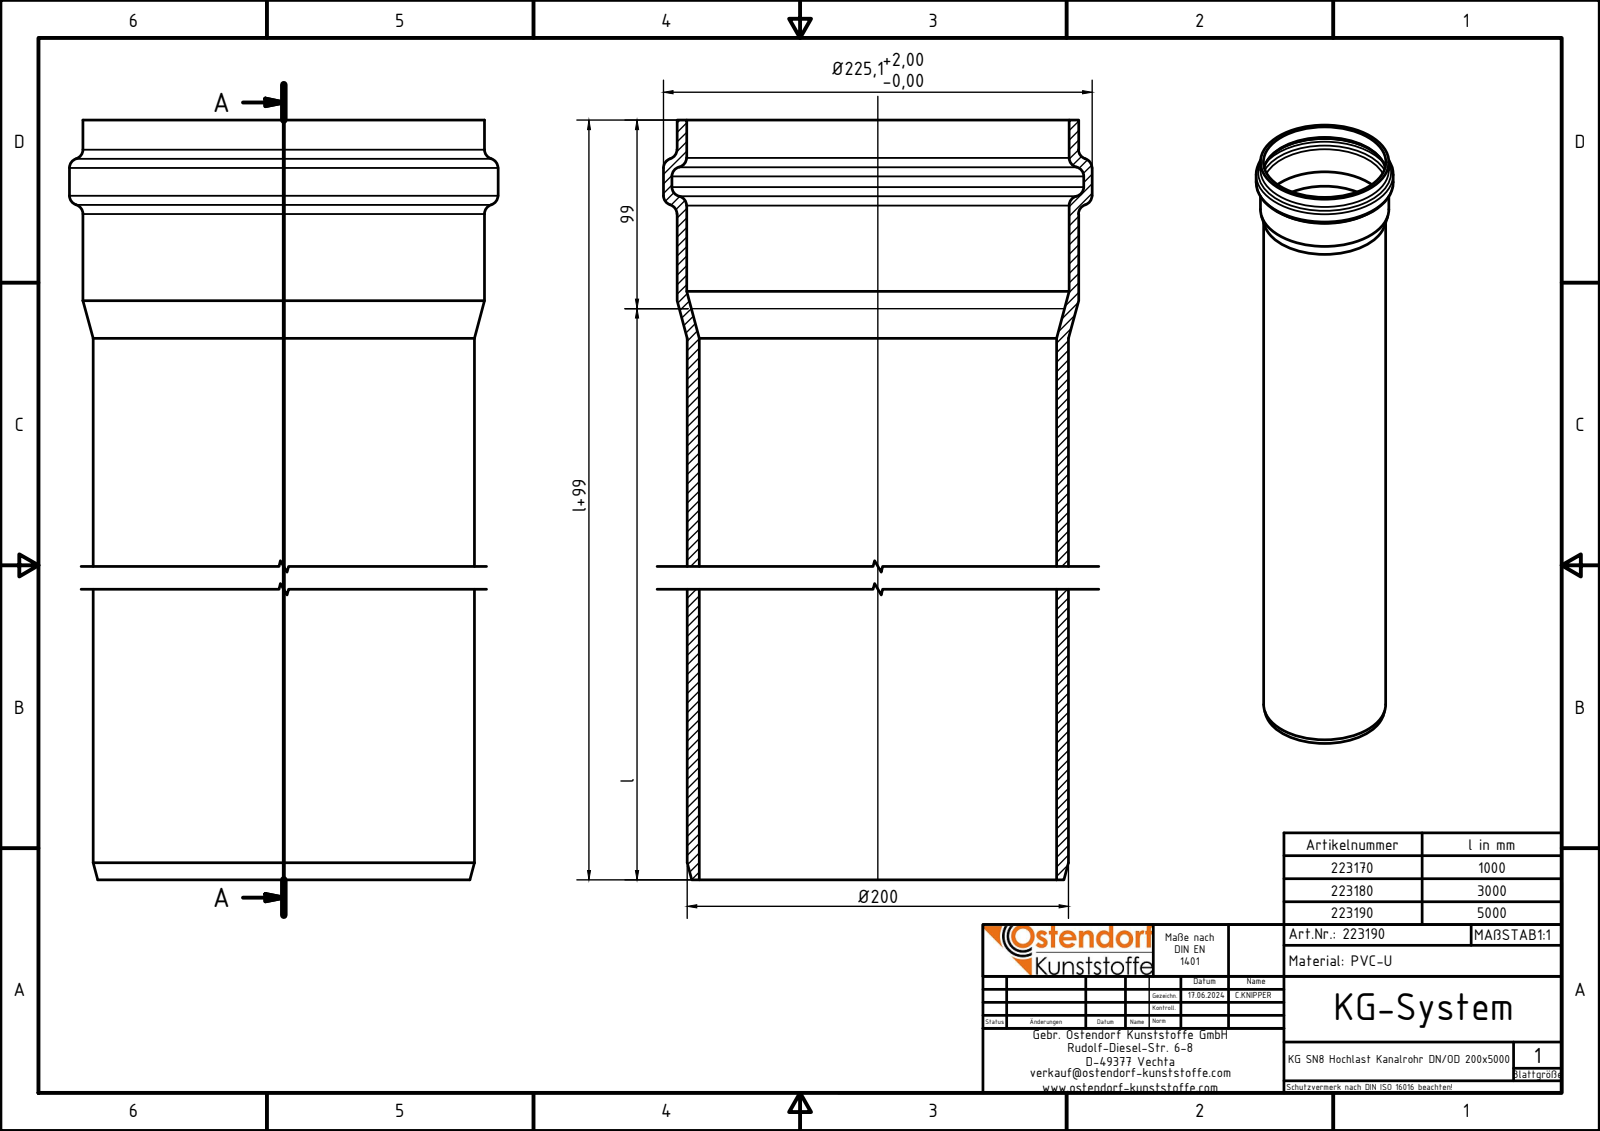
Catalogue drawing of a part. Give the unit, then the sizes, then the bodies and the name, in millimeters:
Units: millimetres
Overall size (bounding box): 5099 × 225.1 × 225.1
Round holes (diameter × count): ⌀187.65 ×1, ⌀200.85 ×1, ⌀216.3 ×1
Round bosses / shafts (diameter × count): ⌀225.1 ×1, ⌀210.85 ×1, ⌀200.25 ×1
Main face-to-face distances: 5099
Volume: 19 550 000 mm³ · Surface area: 6 239 000 mm²
Bodies: 1 solid, 21 faces (2 planar, 8 cylindrical, 11 other)
Part name (STEP PRODUCT): 223190 KGEM Passlängen SN 8 DN_OD 200x5000
STEP written by: Autodesk Inventor 2016 (AUTOMOTIVE_DESIGN)
